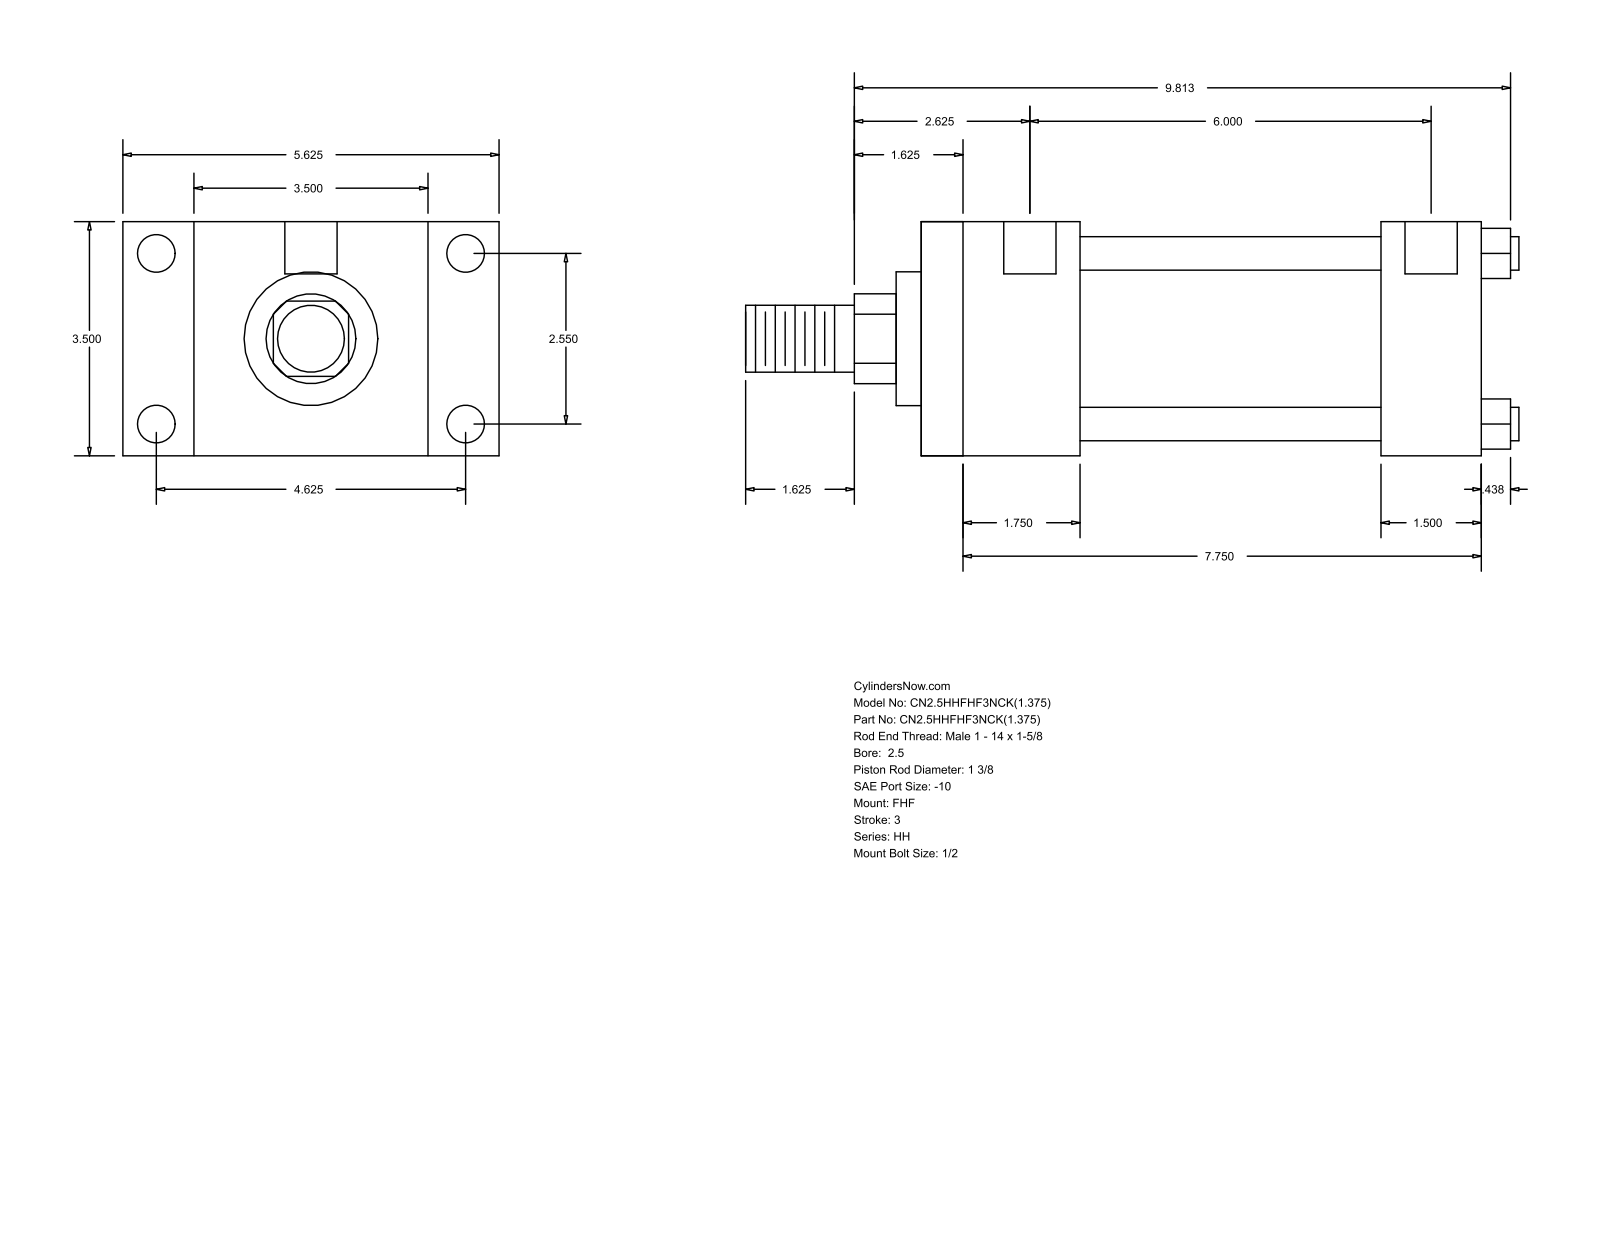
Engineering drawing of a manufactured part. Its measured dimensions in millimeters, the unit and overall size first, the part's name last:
Units: millimetres
Overall size (bounding box): 293.69 × 142.88 × 88.9
Round holes (diameter × count): ⌀5.56 ×4, ⌀14.3 ×4, ⌀19.84 ×2
Round bosses / shafts (diameter × count): ⌀12.7 ×4, ⌀73.03 ×1, ⌀50.8 ×1, ⌀34.92 ×1, ⌀25.4 ×1
Partial cylindrical surfaces — rounded edges, fillets, slot ends (radius × count): R17.06 ×1
Main face-to-face distances: 88.9, 60.32, 26.99, 115.89, 212.72, 152.4, 142.88, 174.63, 114.31, 38.09
Hole centre spacings: 64.76, 117.48, 134.15, 155.57, 1.58, 1.59, 152.4, 153.98
Bodies: 0 solids, 88 faces (60 planar, 28 cylindrical, 0 other)
Part name (STEP PRODUCT): HH_FHF__0250_1.375
STEP written by: GSSL Pune (CONFIG_CONTROL_DESIGN)
